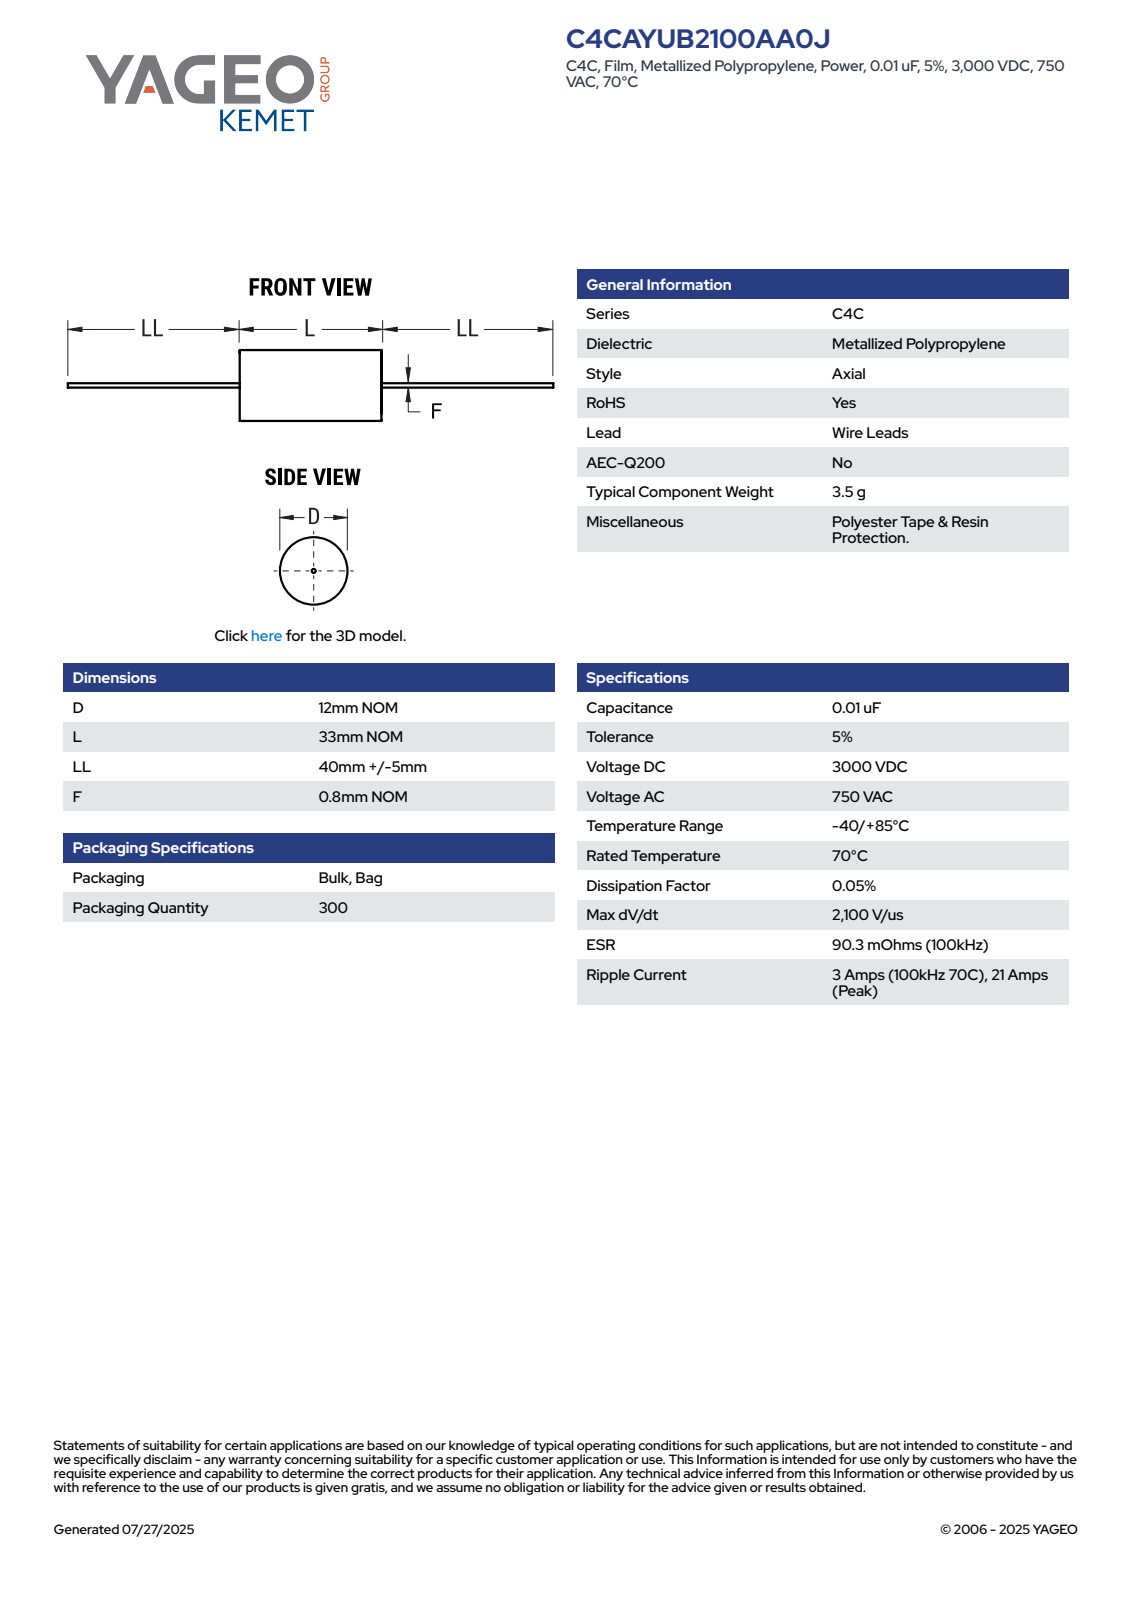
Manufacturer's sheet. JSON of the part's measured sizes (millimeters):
{"part_name": "CFP_ACWF_12X33_D12L33LL45F0.8", "step_written_by": "SolidWorks 2014 (AUTOMOTIVE_DESIGN)", "units": "millimeters", "bodies": {"solids": 2, "faces": 87, "planar": 28, "cylindrical": 28, "other": 31}, "overall_size": [123, 12, 12], "volume_mm3": 3777, "surface_area_mm2": 1922, "round_bosses_or_shafts": [[12, 1], [0.8, 1]], "partial_cylinders_radius": [[5.99, 1]], "face_to_face_distances": [33.01, 33, 45, 78, 44.99, 123, 78.01]}
